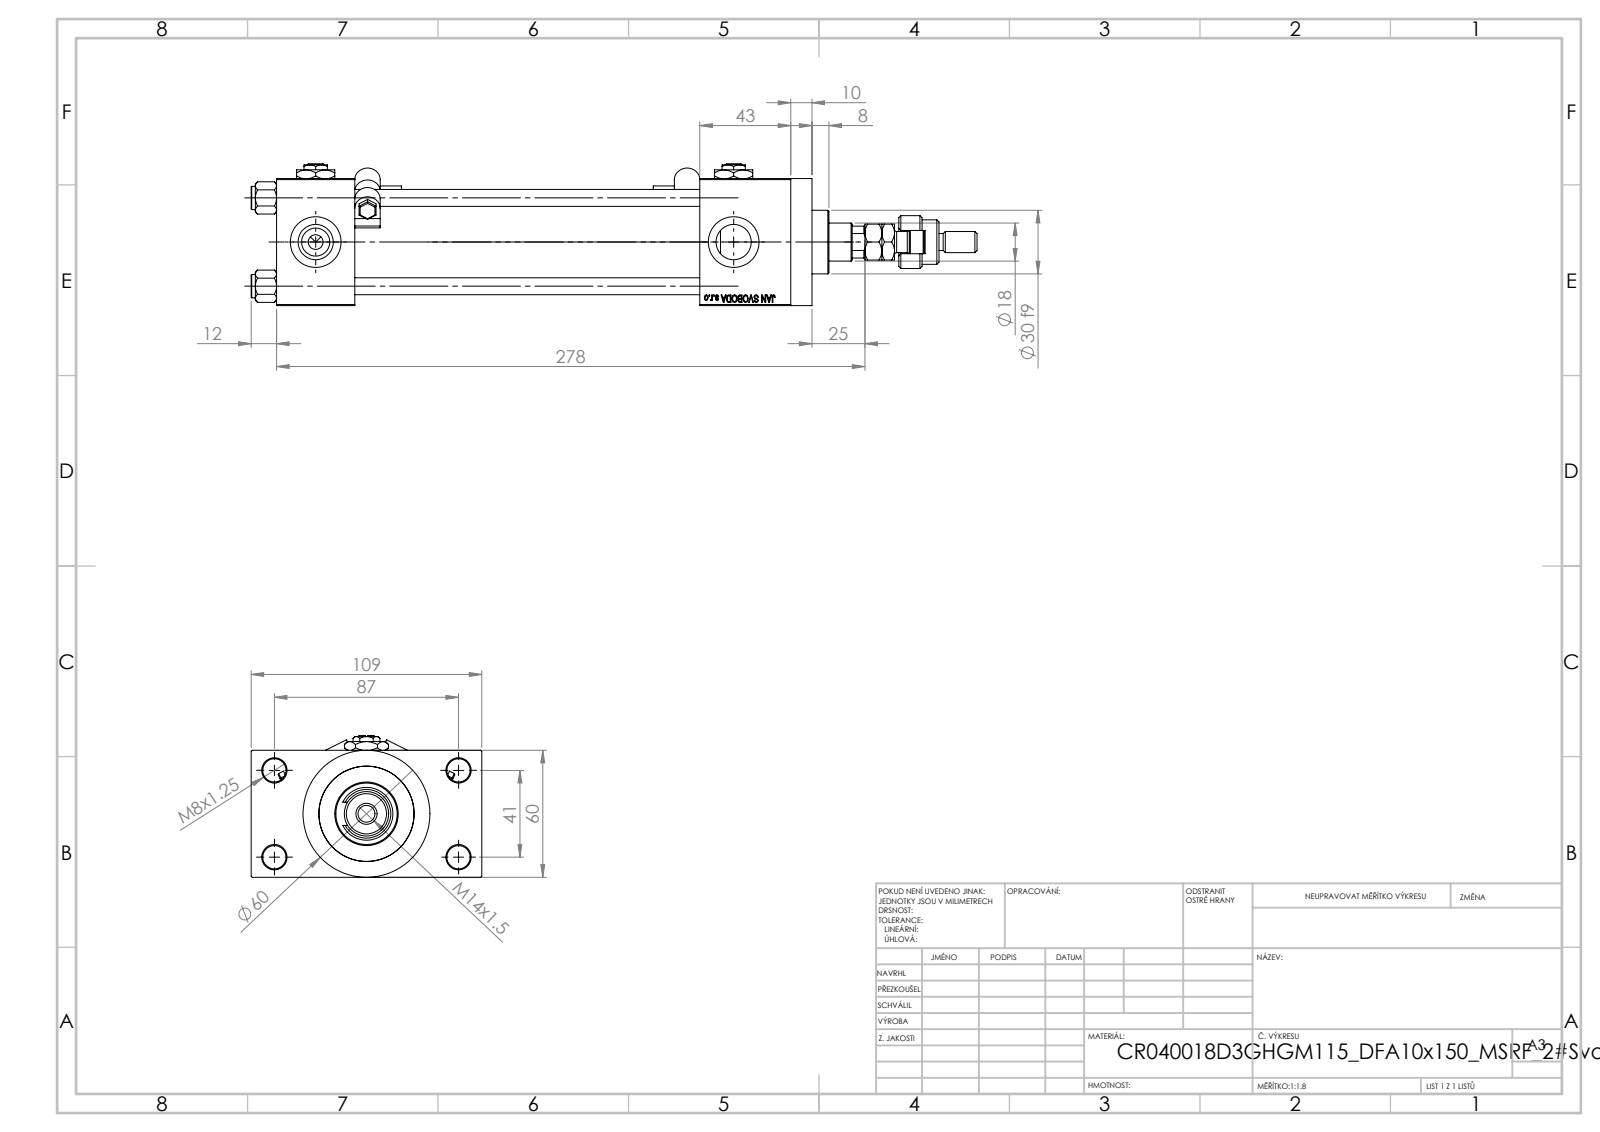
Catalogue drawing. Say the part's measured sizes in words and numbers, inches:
The part is named "MSRF_MSRG1; V215_VC_A; MFA; V215CR_D_Body (+5 more)". Its 3-D file was written by "SolidWorks 2019 (CONFIG_CONTROL_DESIGN)". It is 17 solids with 1354 faces: 610 planar, 140 cylindrical and 604 other. Overall it measures 13.504 by 4.291 by 2.638 inches. Its volume is 37.81 cubic inches and its surface area 278.7 square inches. Round holes: 4 of diameter 0.315, 4 of diameter 0.433, 4 of diameter 0.656, 4 of diameter 0.945, 3 of diameter 0.276, 1 of diameter 0.335, 1 of diameter 0.709, 1 of diameter 0.827, 1 of diameter 1.22, 1 of diameter 1.575, 1 of diameter 1.772. Round bosses or shafts: 4 of diameter 0.433, 2 of diameter 0.197, 2 of diameter 0.098, 1 of diameter 2.362, 1 of diameter 1.811, 1 of diameter 1.181, 1 of diameter 0.984, 1 of diameter 0.63. Partial cylindrical surfaces (rounded edges, fillets, slot ends): 12 of radius 0.02, 4 of radius 0.236, 1 of radius 0.217, 1 of radius 0.335, 1 of radius 0.344. The main face-to-face distances are 2.362, 0.965, 6.417, 7.874, 3.327, 1.457, 9.567, 1.693, 8.11, 2.087. The hole center spacings are 0.892, 1.161, 1.642, 1.856, 1.893, 2.533, 3.011, 1.614.
